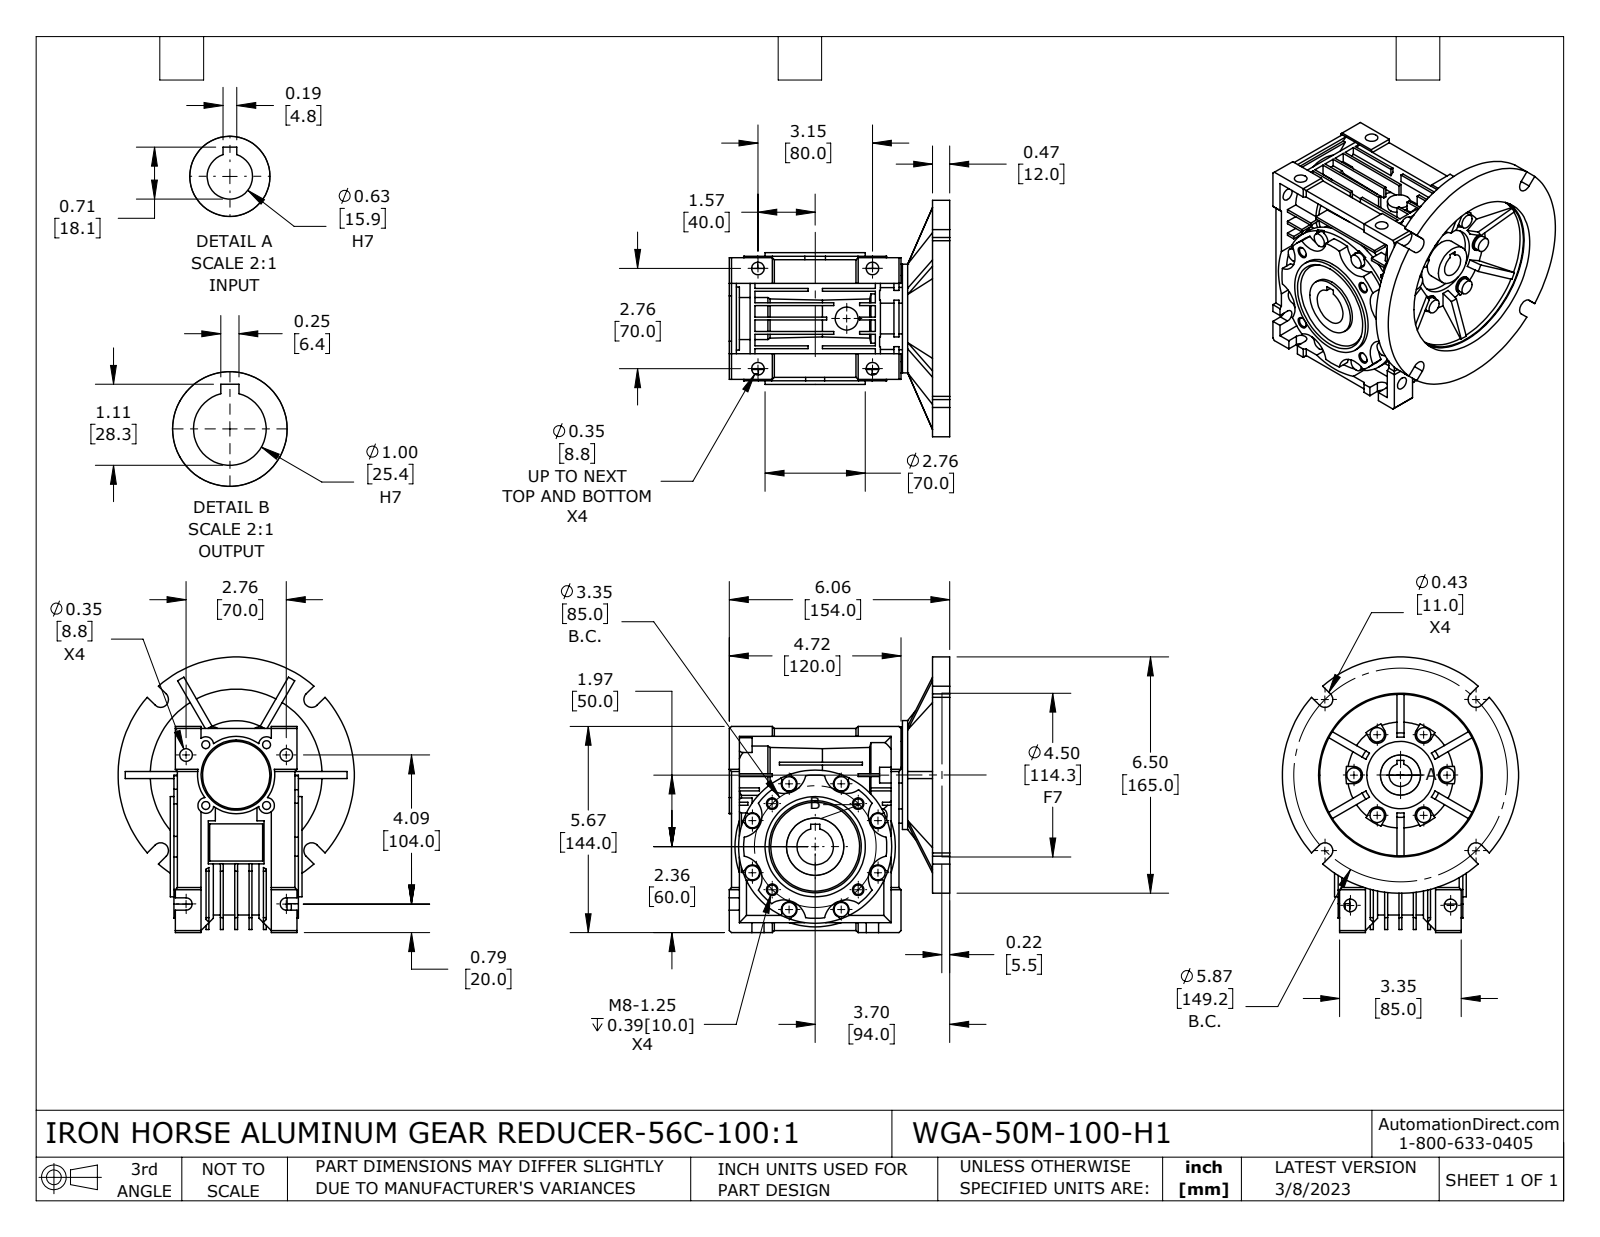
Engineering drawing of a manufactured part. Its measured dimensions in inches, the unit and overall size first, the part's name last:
Units: inches
Overall size (bounding box): 7.579 × 6.496 × 6.063
Round holes (diameter × count): ⌀0.346 ×8, ⌀0.219 ×4, ⌀0.262 ×4, ⌀0.262 ×2, ⌀0.625 ×1, ⌀0.65 ×1, ⌀1 ×1, ⌀1.102 ×1, ⌀1.339 ×1, ⌀1.575 ×1, ⌀1.85 ×1, ⌀4.441 ×1
Round bosses / shafts (diameter × count): ⌀0.394 ×14, ⌀6.496 ×1, ⌀4.213 ×1, ⌀2.992 ×1, ⌀2.756 ×1, ⌀2.402 ×1, ⌀2.165 ×1, ⌀2.126 ×1
Partial cylindrical surfaces — rounded edges, fillets, slot ends (radius × count): R0.217 ×22, R0.236 ×14, R0.591 ×8, R0.61 ×8, R0.167 ×6, R1.811 ×1, R1.878 ×1, R1.969 ×1
Main face-to-face distances: 0.472, 0.394, 0.079, 0.276, 0.315, 0.059, 0.217, 0.787, 2.165, 1.378
Hole centre spacings: 1.181, 1.67, 1.673, 2.366, 2.756, 0.613, 1.484, 1.489
Volume: 72.69 in³ · Surface area: 412.5 in²
Bodies: 4 solids, 954 faces (558 planar, 292 cylindrical, 104 other)
Part name (STEP PRODUCT): WGA-50M-100-H1
STEP written by: SolidWorks 2021 (CONFIG_CONTROL_DESIGN)
